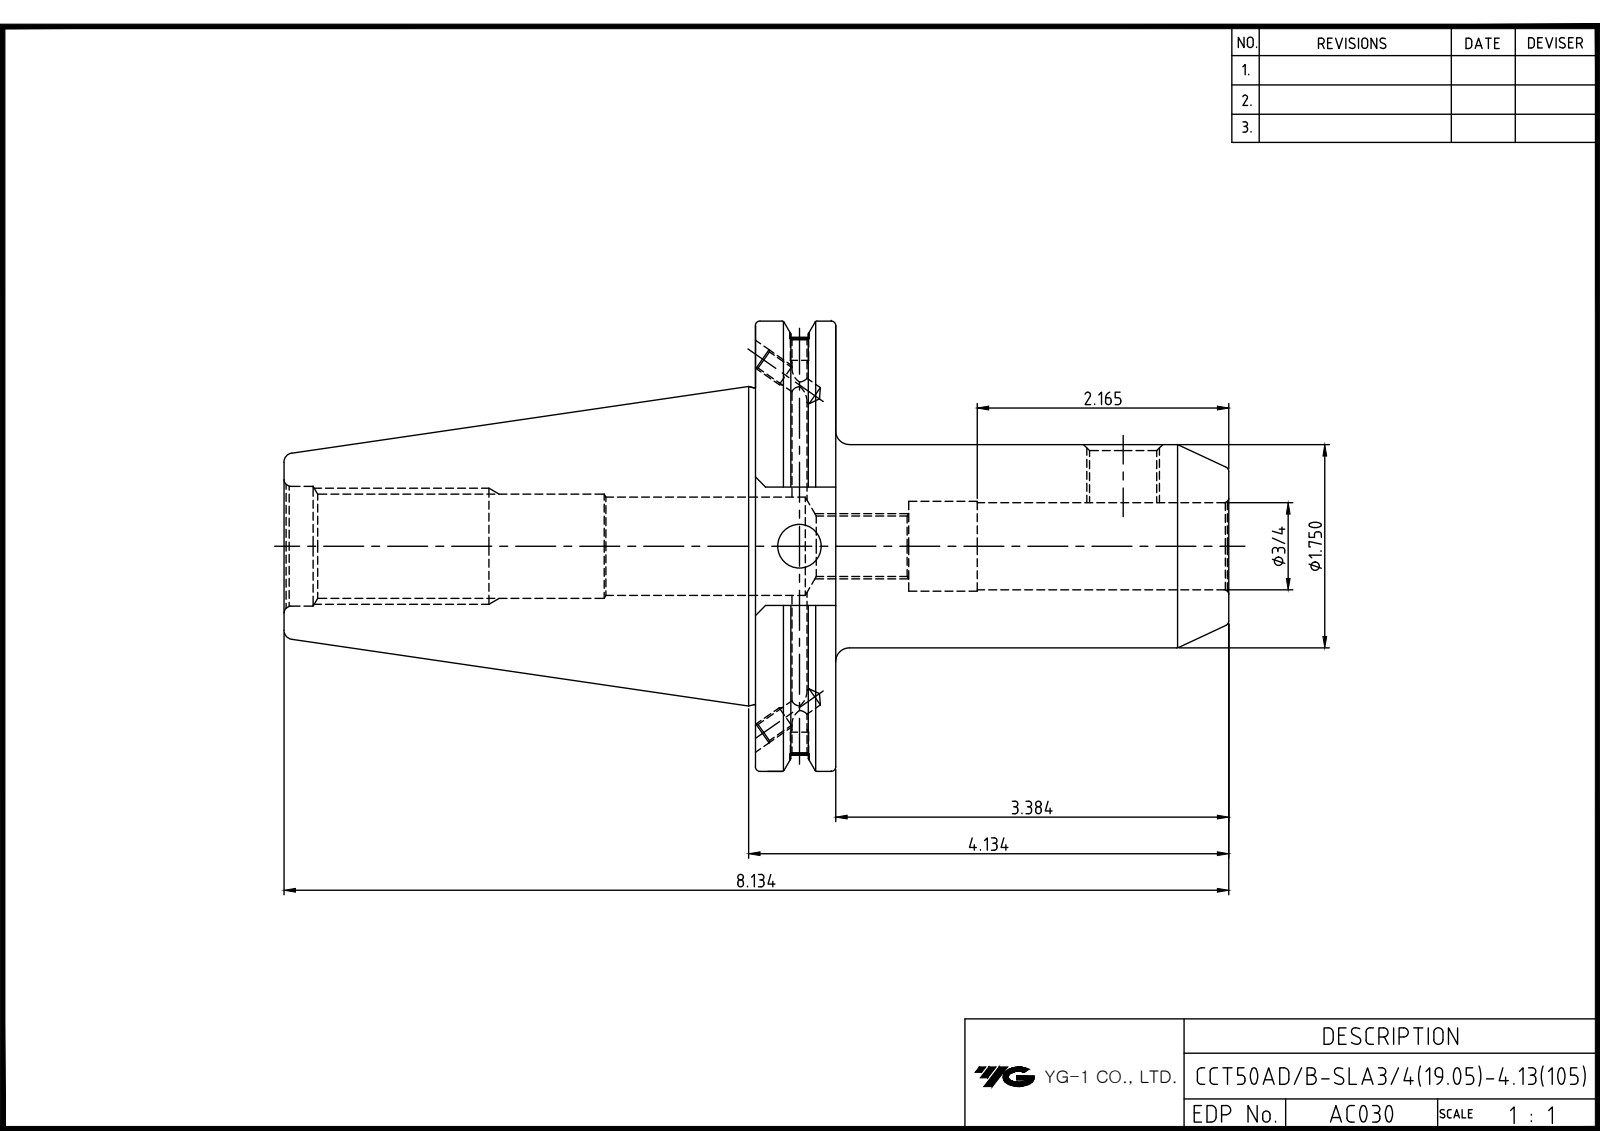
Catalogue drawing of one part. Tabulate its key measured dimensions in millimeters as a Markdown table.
| quantity | value |
| --- | --- |
| part name | LO-CCT50ADB-SLA19.05-105 |
| STEP written by | Autodesk Inventor 2025 (AUTOMOTIVE_DESIGN) |
| units | millimeters |
| bodies | 1 solid, 90 faces (39 planar, 27 cylindrical, 24 other) |
| overall size | 206.6 × 98.42 × 94.69 |
| volume | 429 399 mm³ |
| surface area | 61 582 mm² |
| round holes (diameter × count) | 3.24 × 2, 4.13 × 2, 4.2 × 2, 5 × 2, 9.53 × 1, 12.57 × 1, 14.35 × 1, 19.05 × 1, 20.25 × 1, 21.97 × 1, 26.2 × 1 |
| round bosses / shafts (diameter × count) | 98.42 × 1, 91.29 × 1, 69.25 × 1, 44.45 × 1 |
| main face-to-face distances | 17.55, 103.1, 103.5, 120.65, 206.6, 85.95, 73.03, 25.9, 0.4, 17.15 |
